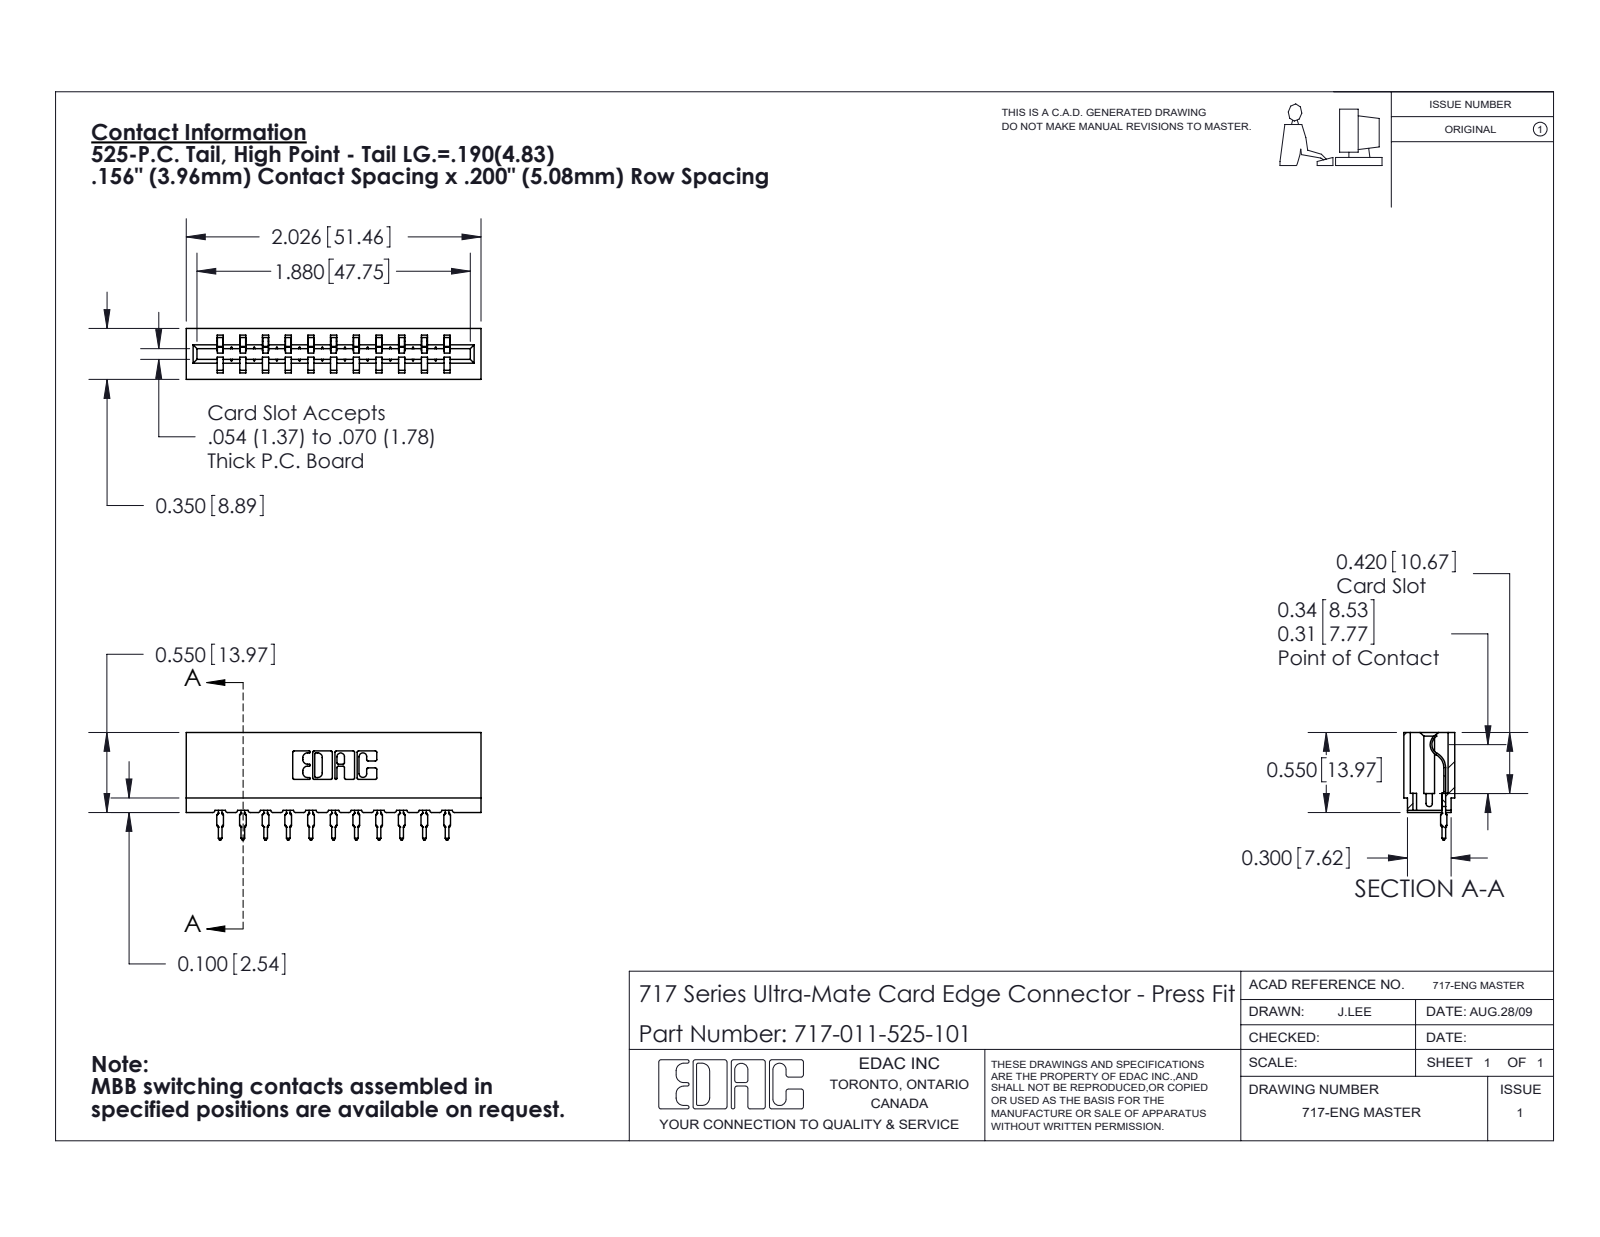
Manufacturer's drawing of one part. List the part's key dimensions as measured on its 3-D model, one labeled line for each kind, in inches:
Part name (STEP PRODUCT): 745-292-001_525; 717-011-525-101; 717 Part_Insulator Option - 06
STEP written by: SolidWorks 2020 (CONFIG_CONTROL_DESIGN)
Units: inches
Bodies: 12 solids, 1337 faces (802 planar, 249 cylindrical, 286 other)
Overall size (bounding box): 2.026 × 0.739 × 0.35
Volume: 0.273 in³ · Surface area: 9.173 in²
Partial cylindrical surfaces — rounded edges, fillets, slot ends (radius × count): R0.01 ×22, R0.015 ×22, R0.021 ×22, R0.007 ×6, R0.031 ×6, R0.005 ×4, R0.011 ×4, R0.026 ×3
Main face-to-face distances: 0.212, 0.156, 0.138, 0.468, 0.624, 0.35, 0.312, 0.198, 0.312, 0.042
